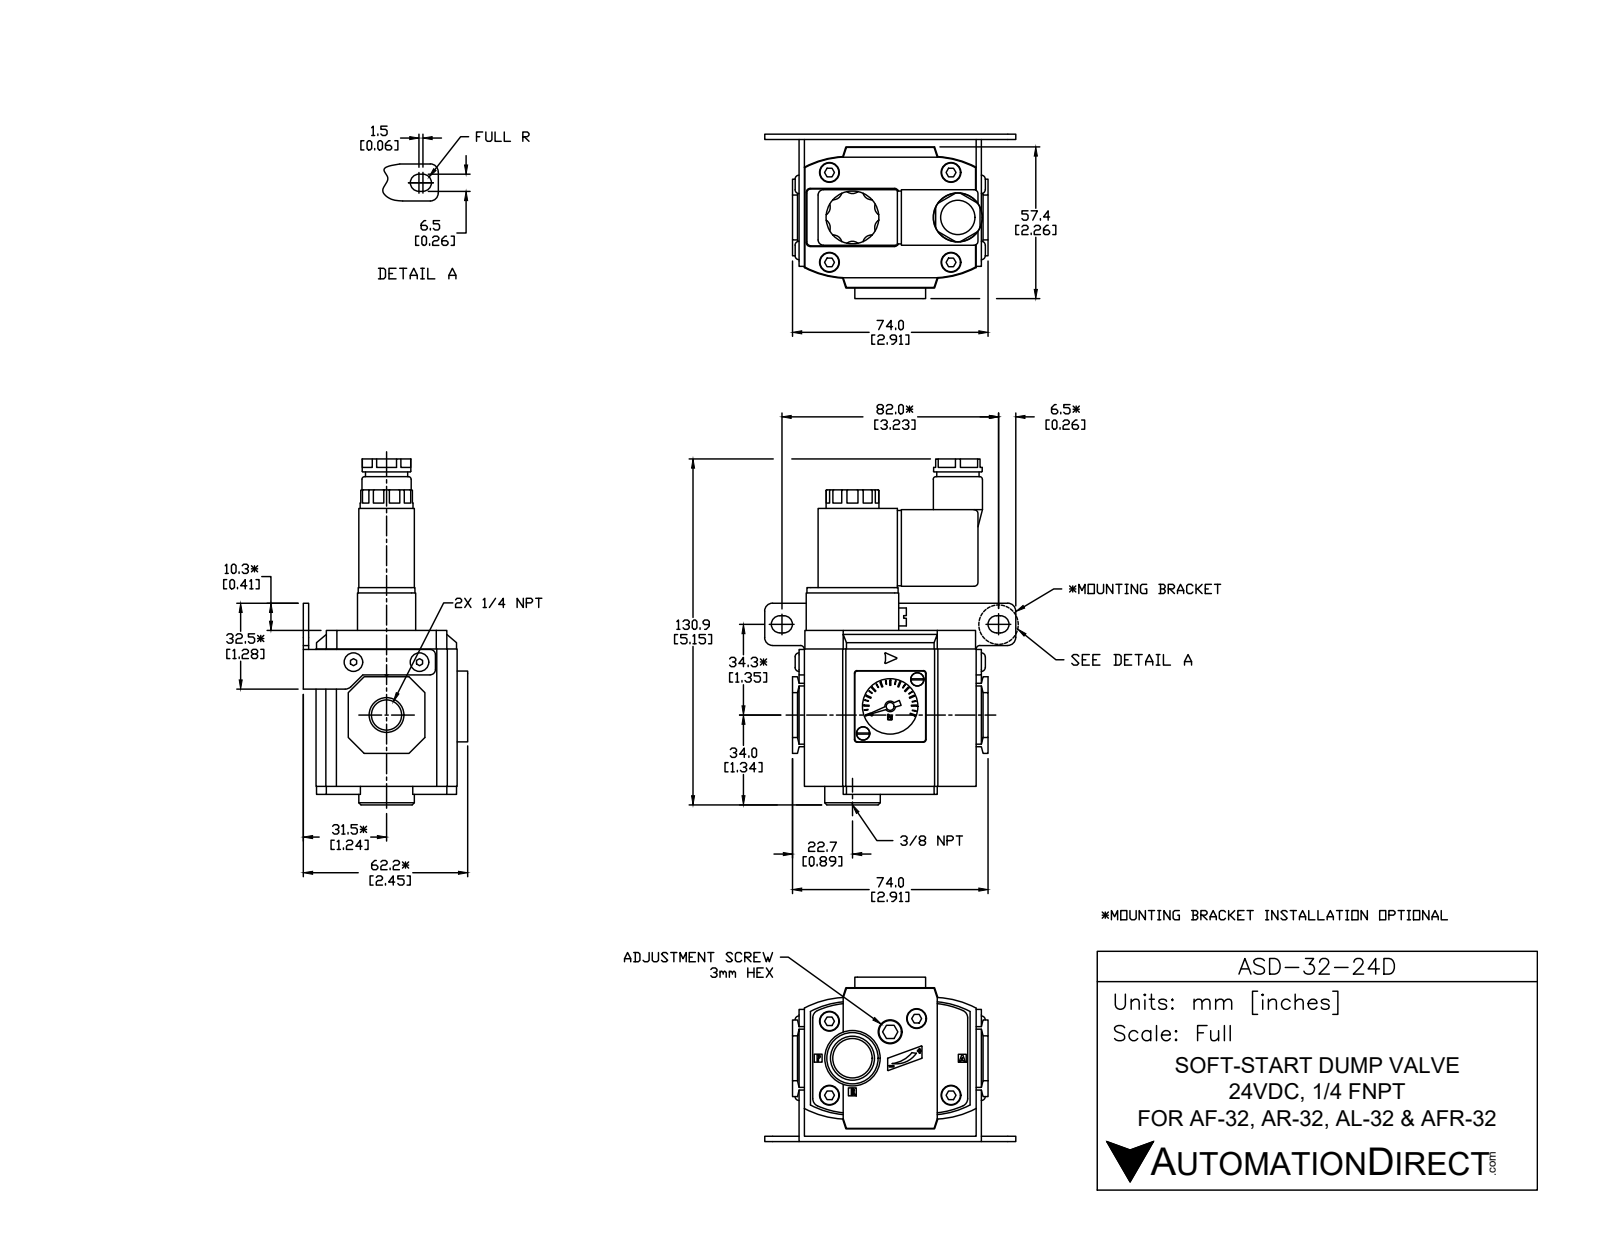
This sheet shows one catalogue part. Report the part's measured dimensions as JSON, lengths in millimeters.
{"part_name": "ASD-32-24D", "step_written_by": "SolidWorks 2015 (CONFIG_CONTROL_DESIGN)", "units": "millimeters", "bodies": {"solids": 22, "faces": 550, "planar": 343, "cylindrical": 164, "other": 43}, "overall_size": [130.9, 95, 62.9], "volume_mm3": 256716, "surface_area_mm2": 60550, "round_holes": [[4, 8], [7.5, 8], [3, 2], [21, 2], [8.5, 1], [9, 1], [11.13, 1], [13, 1], [14.95, 1]], "round_bosses_or_shafts": [[7.1, 8], [2.5, 2], [20, 1], [18.6, 1], [18.4, 1], [16, 1], [4, 1]], "partial_cylinders_radius": [[1.5, 10], [3.16, 10], [1, 6], [3, 6], [0.73, 4], [1.25, 4], [3.25, 4], [34.8, 4]], "face_to_face_distances": [3, 2, 52, 59, 7, 21, 13.2, 34.2, 16.2, 37.2], "hole_center_spacings": [3, 31, 46, 46.1, 55.47, 14.5, 16.48, 17.2]}
